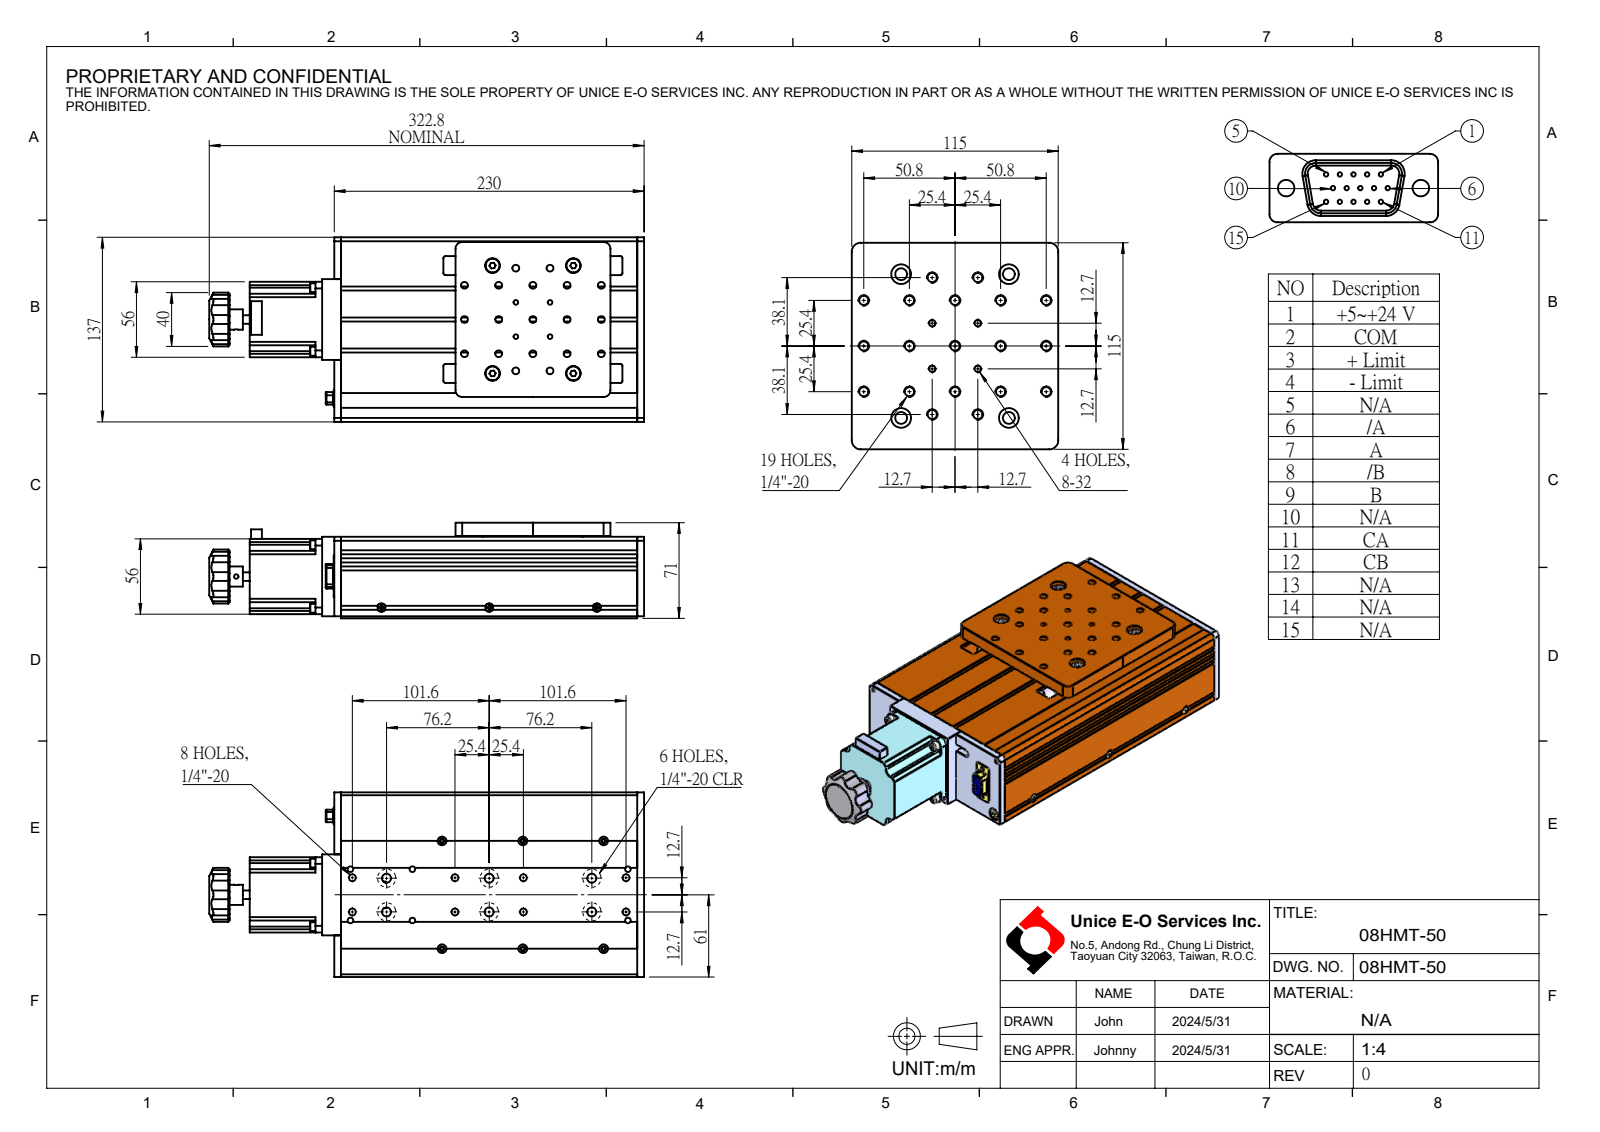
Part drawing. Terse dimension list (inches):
name: 08HMT-50
written by: SolidWorks 2016 (AUTOMOTIVE_DESIGN)
unit: in
bodies: 0 solids, 736 faces (353 planar, 268 cylindrical, 115 other)
size: 12.709 × 5.394 × 2.795
holes: 27× ⌀0.201, 15× ⌀0.031, 6× ⌀0.165, 6× ⌀0.256, 6× ⌀0.266, 4× ⌀0.136, 4× ⌀0.433, 2× ⌀0.079, 2× ⌀0.089, 2× ⌀0.12, 2× ⌀0.13, 1× ⌀0.984
bosses: 4× ⌀0.256, 3× ⌀0.228, 2× ⌀0.303, 2× ⌀0.276, 1× ⌀0.591, 1× ⌀0.551, 1× ⌀0.25
rounds: 8× R0.02, 8× R0.157, 8× R0.197, 8× R0.292, 7× R0.059, 4× R0.079, 4× R0.177, 3× R0.118
face distances: 0.079, 5.315, 2.382, 0.059, 5.236, 0.413, 2.323, 0.197, 2.795, 8.858
hole spacings: 1.581, 1, 0.707, 2.236, 1.414, 2.55, 0.112, 2
